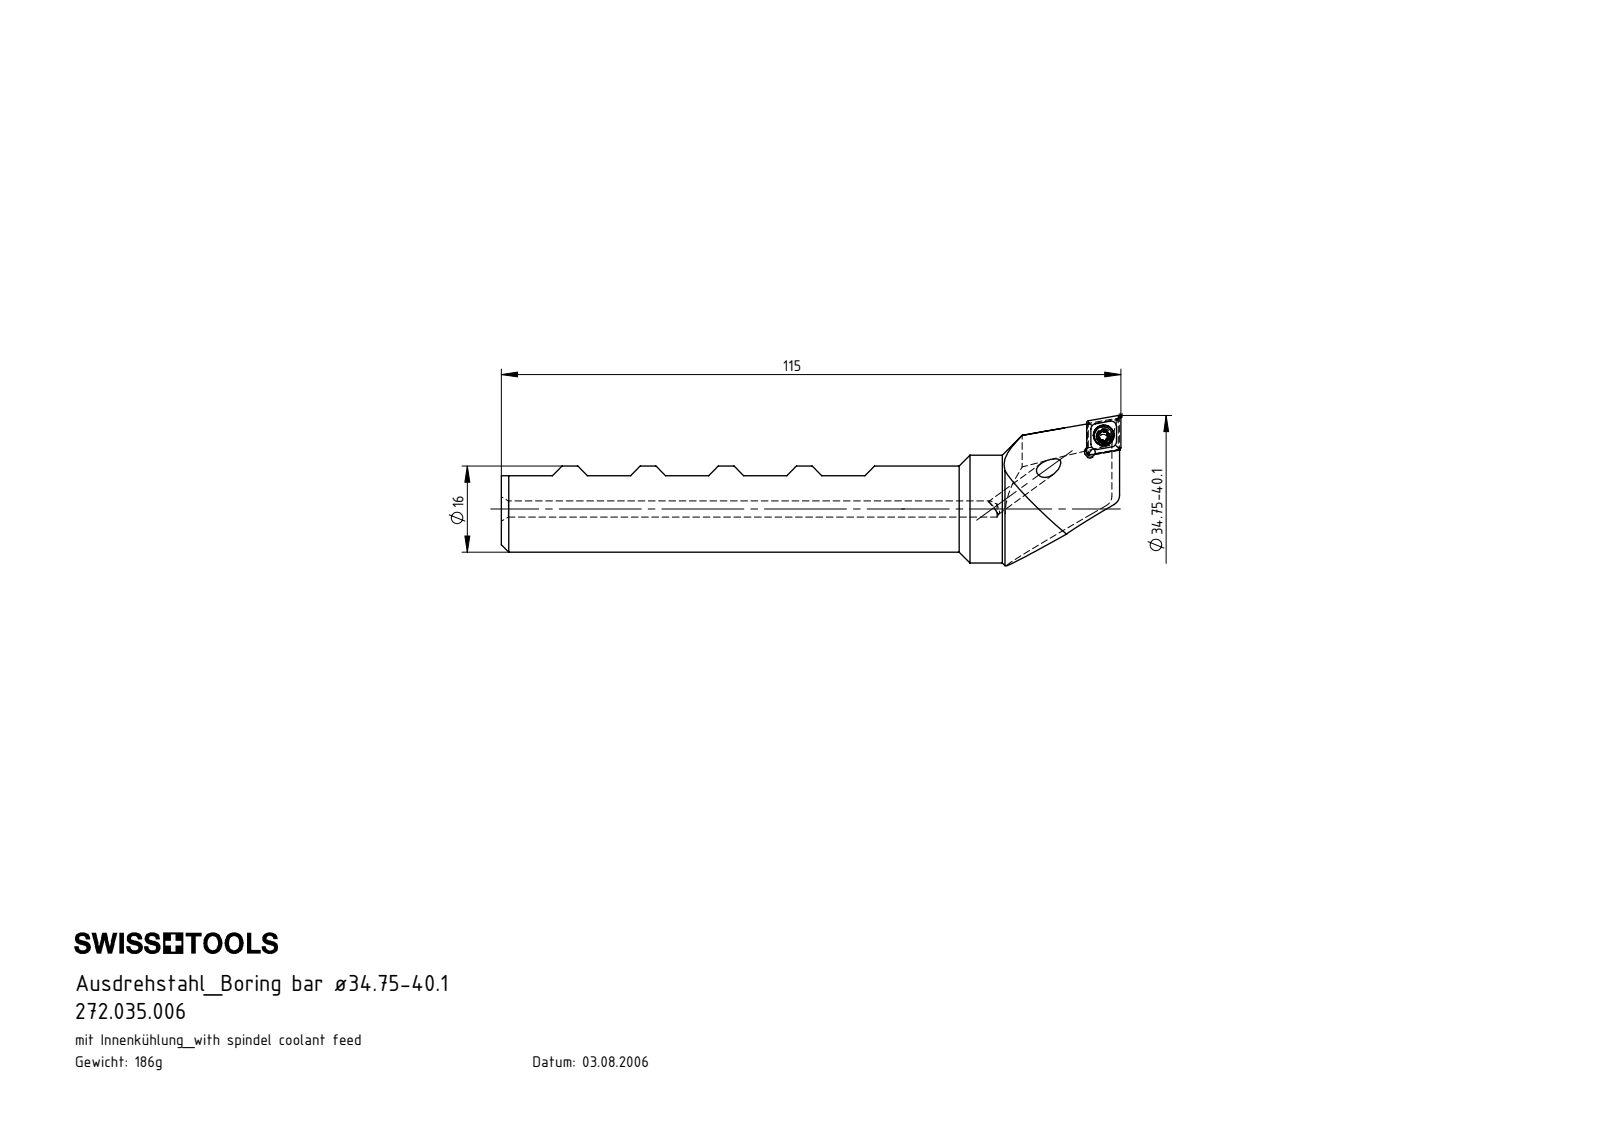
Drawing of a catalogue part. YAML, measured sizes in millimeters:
part_name: "CCMT060204; B35-WCA.K11.115_A; WCA-ER2.001.006_A; B35-WCA.K11.115"
step_written_by: "SolidWorks 2017 (CONFIG_CONTROL_DESIGN)"
units: millimeters
bodies: {solids: 3, faces: 136, planar: 42, cylindrical: 39, other: 55}
overall_size: [115, 27.88, 22.08]
volume: 23662
surface_area: 7817
round_holes:
  - {diameter: 3, count: 2}
  - {diameter: 2, count: 1}
  - {diameter: 2.05, count: 1}
  - {diameter: 2.8, count: 1}
  - {diameter: 3.85, count: 1}
round_bosses_or_shafts:
  - {diameter: 20, count: 1}
  - {diameter: 16, count: 1}
  - {diameter: 3.4, count: 1}
  - {diameter: 2.5, count: 1}
partial_cylinders:
  - {radius: 0.21, count: 6}
  - {radius: 0.36, count: 5}
  - {radius: 0.36, count: 1}
  - {radius: 2, count: 1}
  - {radius: 10.5, count: 1}
  - {radius: 12, count: 1}
face_to_face_distances: [10.25, 11.81, 9.63, 2.18, 20.5, 20.51, 30.76, 30.75, 10.26, 41.01]
hole_center_spacings: [3.89, 3.99]
